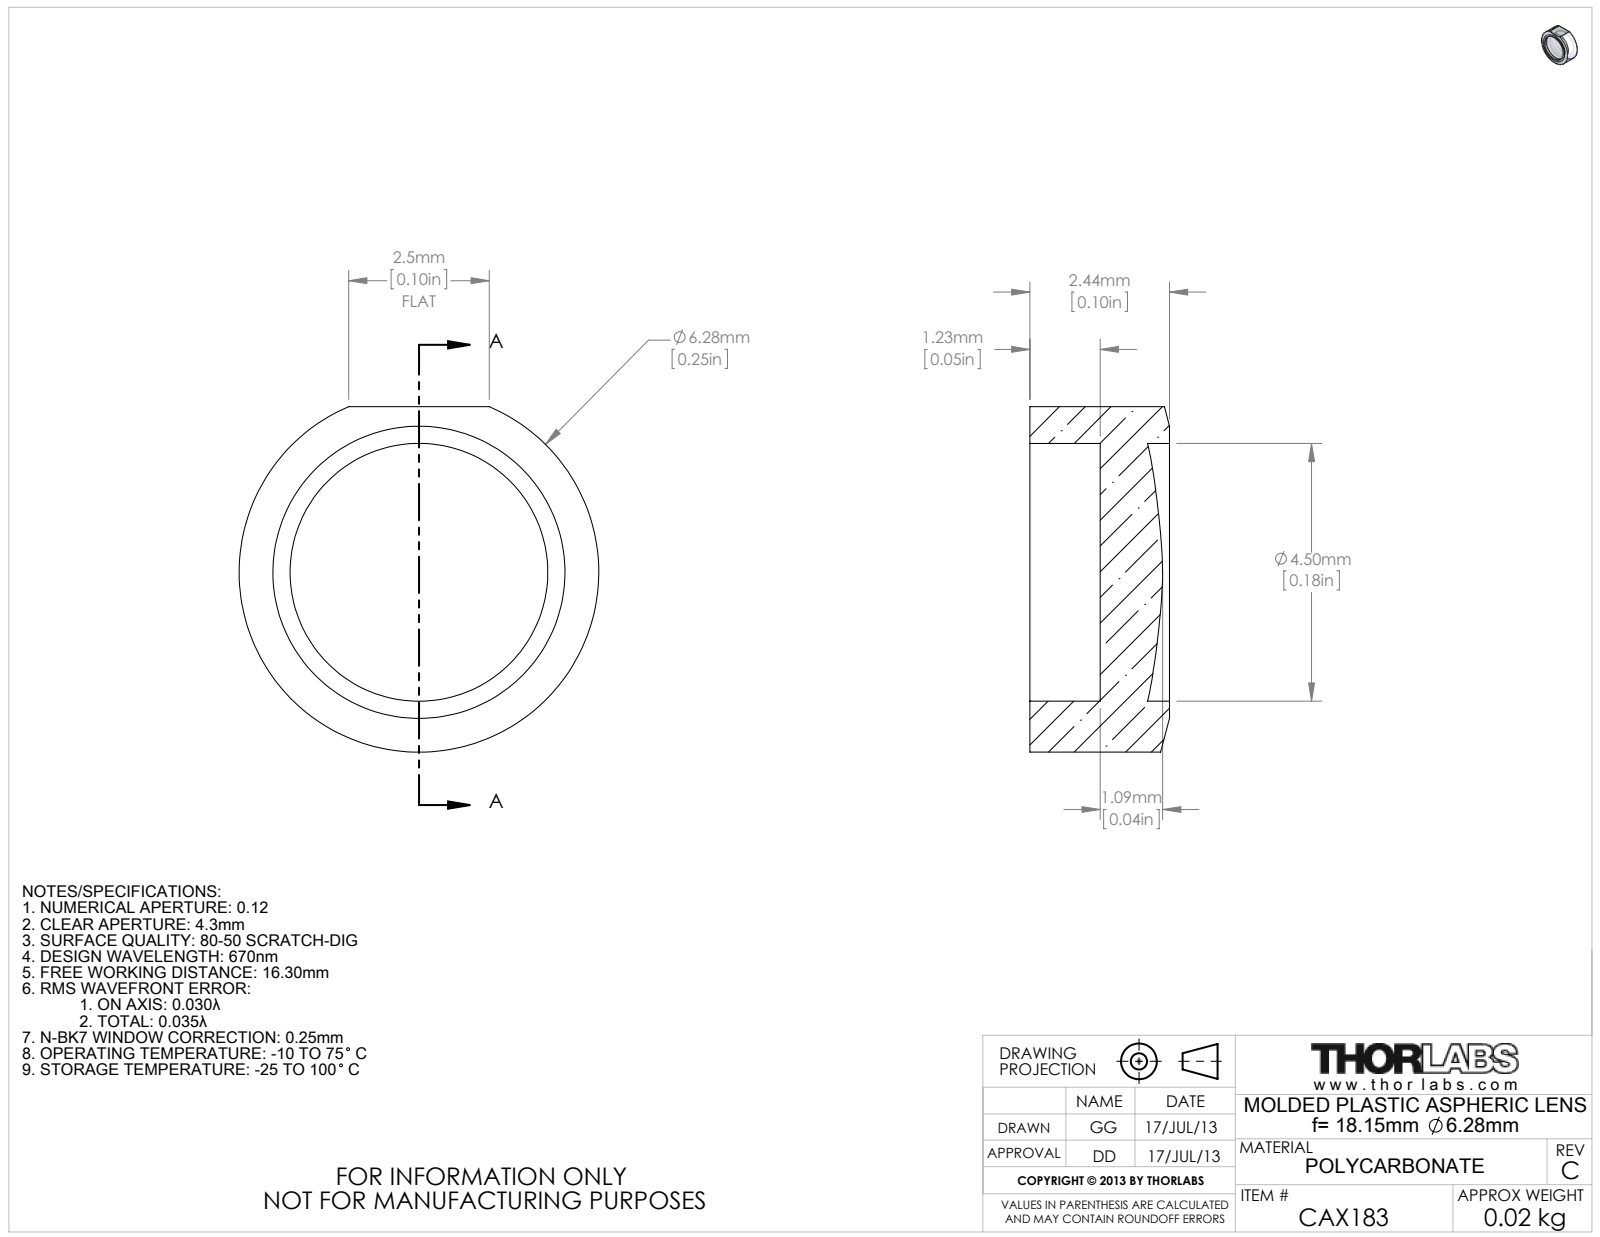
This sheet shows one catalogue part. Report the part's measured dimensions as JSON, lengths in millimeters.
{"part_name": "2013-E0W", "step_written_by": "SolidWorks 2012 (CONFIG_CONTROL_DESIGN)", "units": "millimeters", "bodies": {"solids": 1, "faces": 13, "planar": 4, "cylindrical": 5, "other": 4}, "overall_size": [6.3, 6, 2.4], "volume_mm3": 50, "surface_area_mm2": 130, "round_holes": [[4.5, 1]], "round_bosses_or_shafts": [[6.3, 1]], "face_to_face_distances": [1.2, 1.2, 2.4]}
